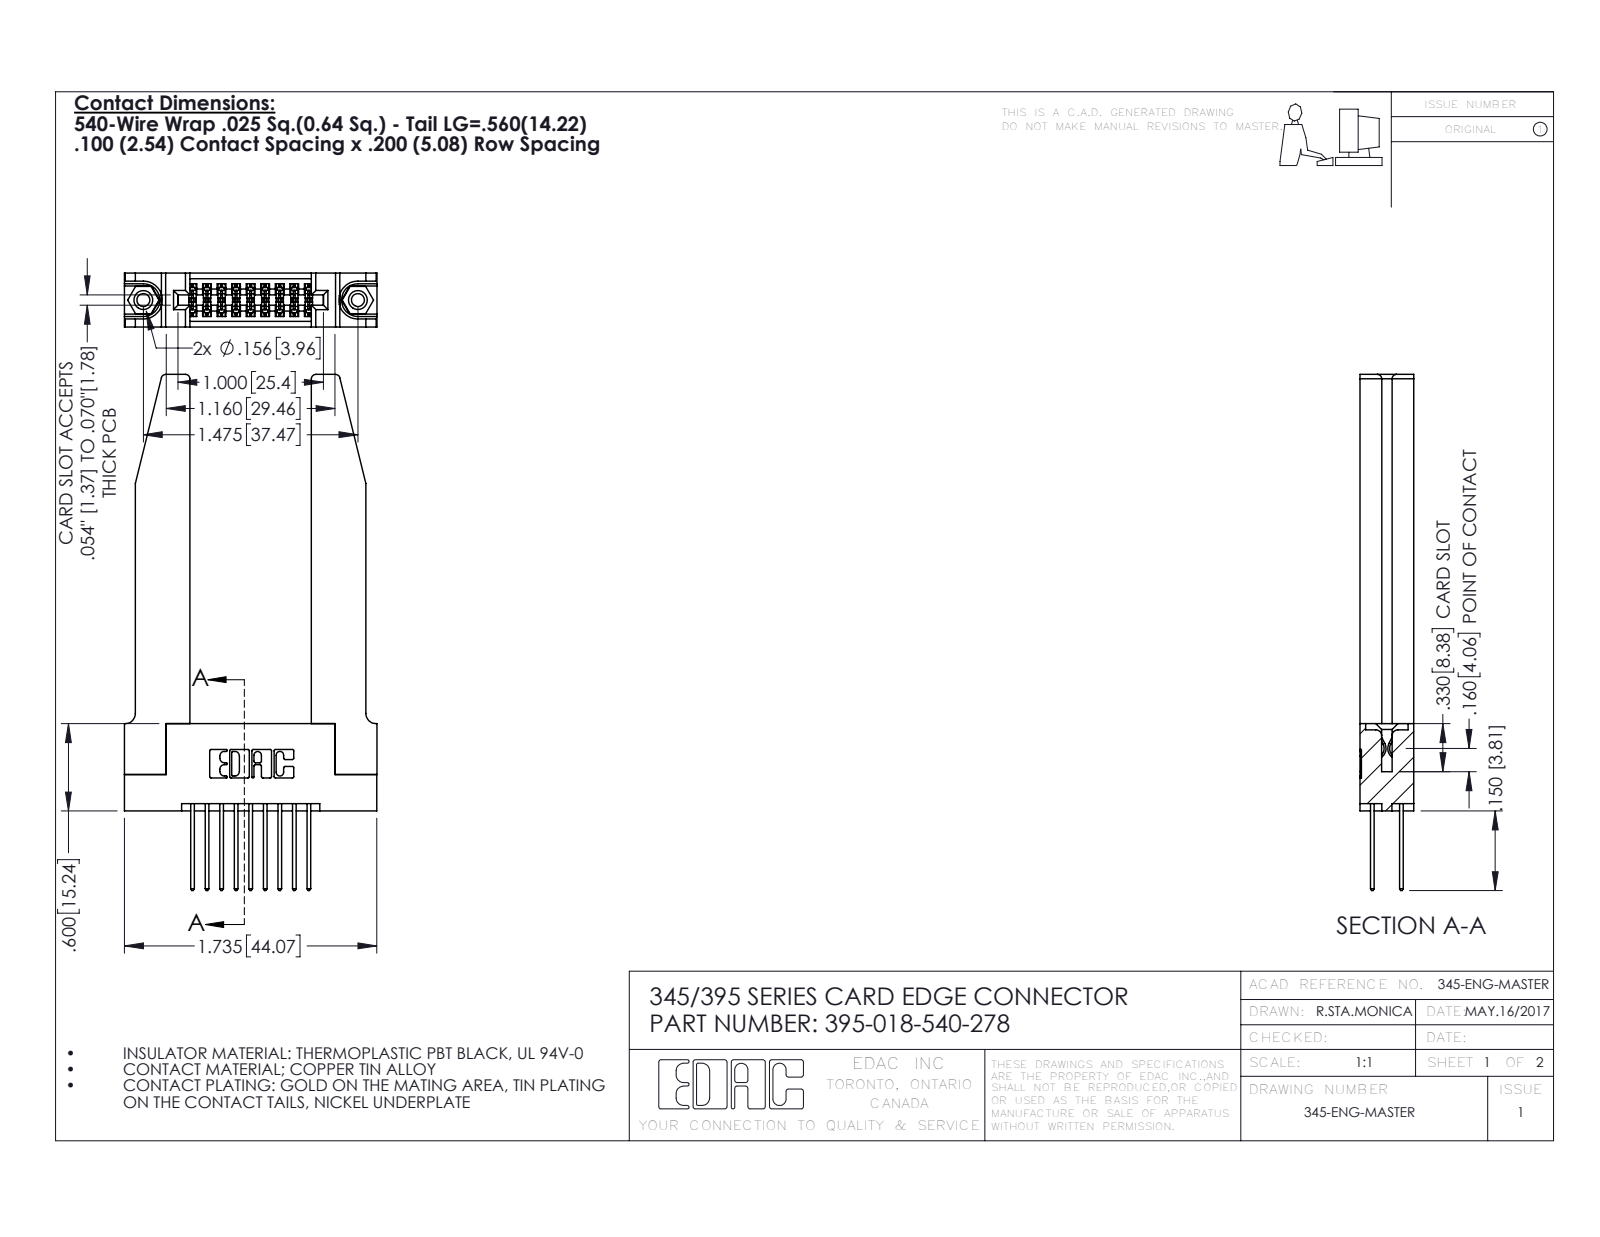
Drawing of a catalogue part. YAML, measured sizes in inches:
part_name: "345 Part_Flush Mounting Lugs - 0.156 Dia-TH; 395-018-540-278; 345-292-001_345-293-140; 345-250-001_345-250-001-102 (+1 more)"
step_written_by: "SolidWorks 2016 (CONFIG_CONTROL_DESIGN)"
units: inches
bodies: {solids: 23, faces: 1260, planar: 816, cylindrical: 392, other: 52}
overall_size: [3.547, 1.736, 0.37]
volume: 0.721
surface_area: 19.37
round_holes:
  - {diameter: 0.089, count: 2}
  - {diameter: 0.125, count: 2}
  - {diameter: 0.156, count: 2}
  - {diameter: 0.064, count: 1}
round_bosses_or_shafts:
  - {diameter: 0.155, count: 2}
partial_cylinders:
  - {radius: 0.006, count: 27}
  - {radius: 0.01, count: 22}
  - {radius: 0.01, count: 18}
  - {radius: 0.03, count: 8}
  - {radius: 0.007, count: 6}
  - {radius: 0.031, count: 6}
  - {radius: 0.026, count: 3}
  - {radius: 0.014, count: 2}
face_to_face_distances: [0.37, 0.072, 0.298, 0.2, 0.148, 0.15, 0.077, 0.22, 0.098, 0.272]
hole_center_spacings: [0.27, 1.244, 1.475]
